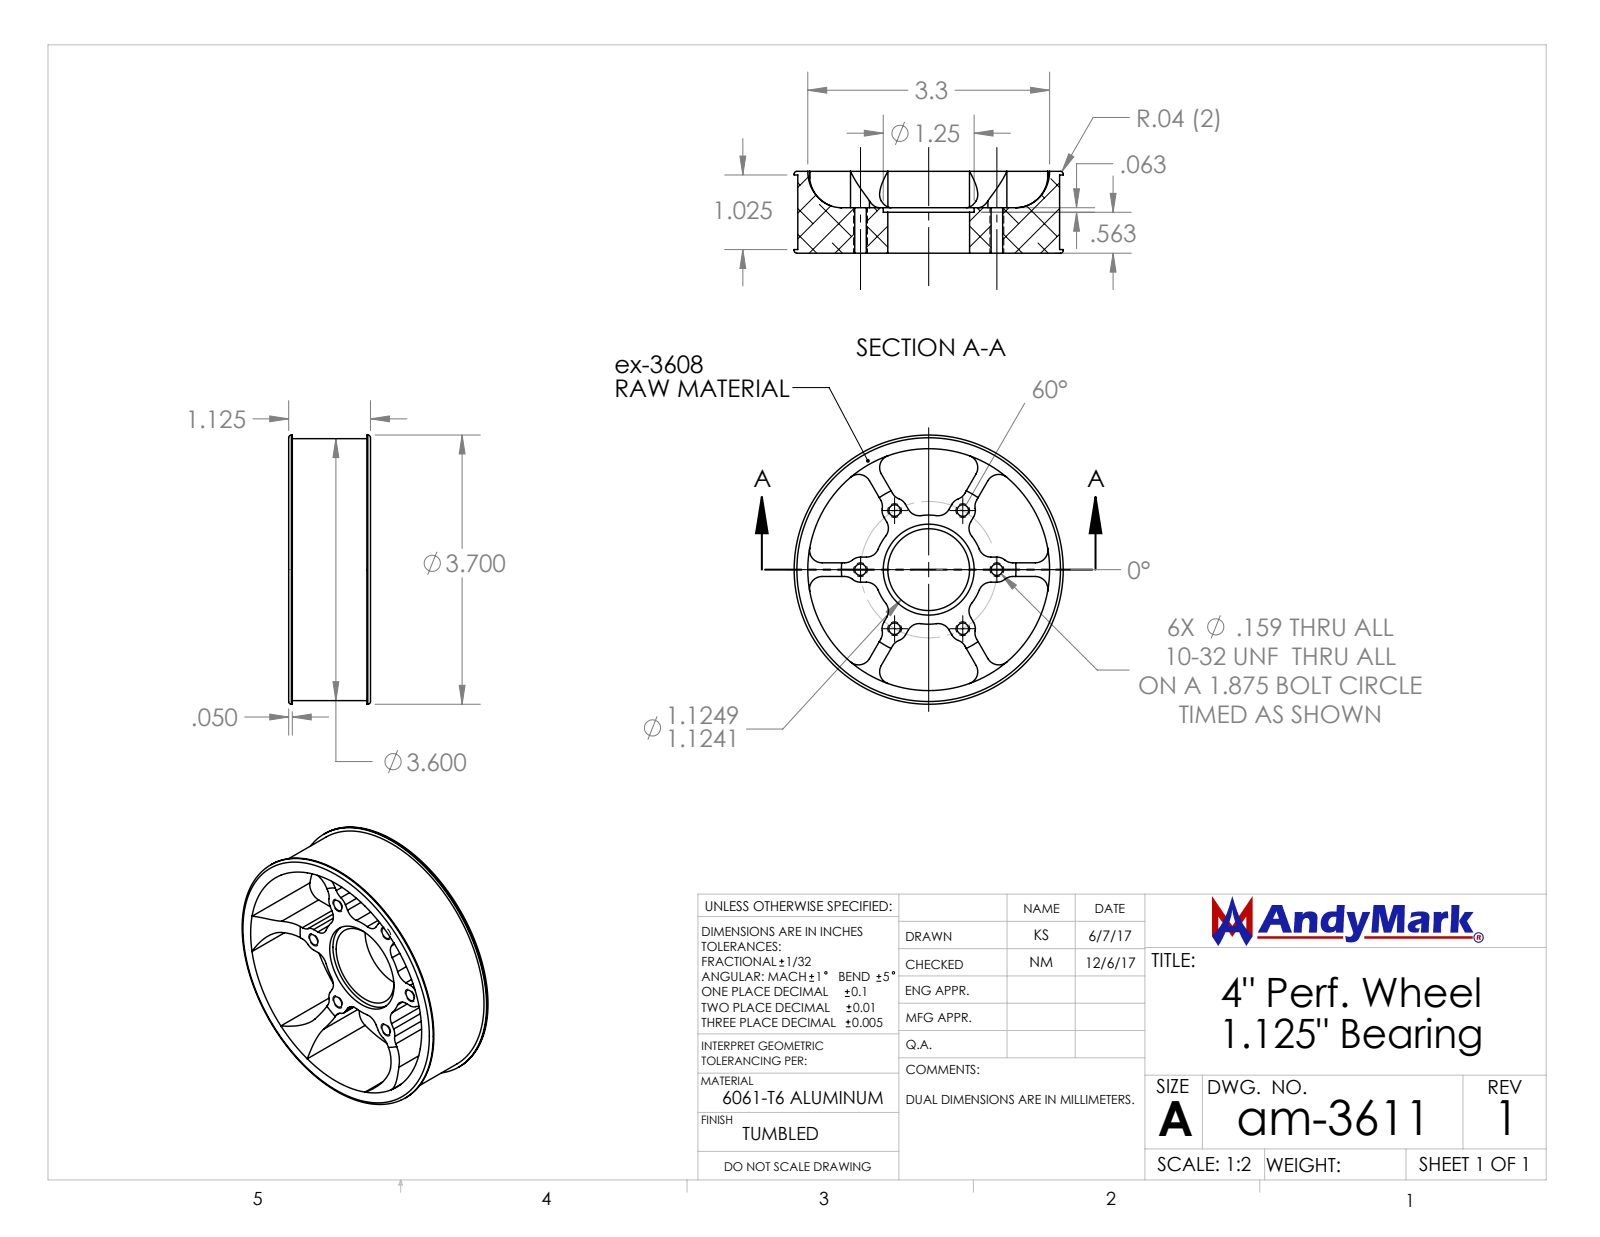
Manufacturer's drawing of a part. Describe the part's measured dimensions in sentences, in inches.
The part is named "am-3611 4IN Extrusion Performance Wheel 1125 Bearing". Its 3-D file was written by "SolidWorks 2017 (CONFIG_CONTROL_DESIGN)". It is 1 solid with 132 faces: 30 planar, 92 cylindrical and 10 other. Overall it measures 3.7 by 3.7 by 1.125 inches. Its volume is 3.126 cubic inches and its surface area 44.78 square inches. Round holes: 6 of diameter 0.159, 1 of diameter 1.124, 1 of diameter 1.25. Round bosses or shafts: 1 of diameter 3.7, 1 of diameter 3.6. Partial cylindrical surfaces (rounded edges, fillets, slot ends): 42 of radius 0.172, 1 of radius 0.75, 1 of radius 1.662, 1 of radius 1.663. The main face-to-face distances are 1.125, 0.625, 0.5, 0.187, 0.05, 1.075, 0.575, 1.025, 0.45, 0.563. The hole center spacings are 0.937, 1.624, 1.875, 0.938.
